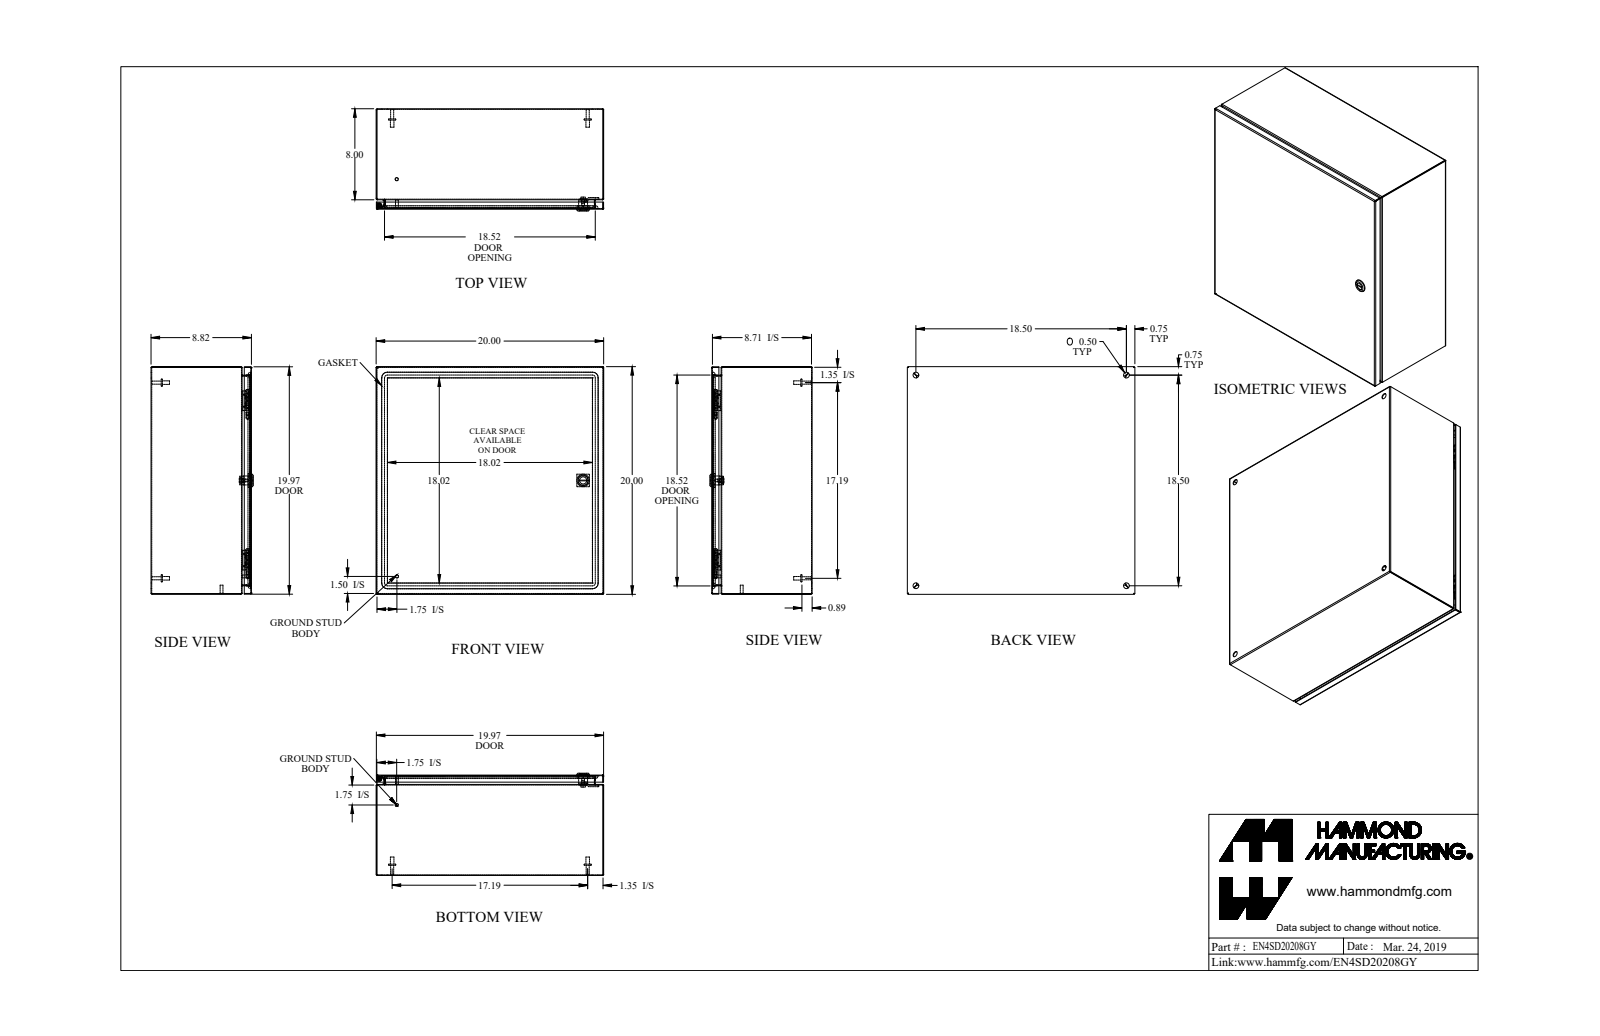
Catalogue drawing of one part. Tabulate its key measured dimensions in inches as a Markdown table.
| quantity | value |
| --- | --- |
| part name | EN4SD20208GY_Default |
| STEP written by | SolidWorks 2019 (CONFIG_CONTROL_DESIGN) |
| units | inches |
| bodies | 21 solids, 634 faces (285 planar, 213 cylindrical, 136 other) |
| overall size | 20 × 20 × 8.982 |
| volume | 98.82 in³ |
| surface area | 3 368 in² |
| round holes (diameter × count) | 0.5 × 4, 0.172 × 1, 0.232 × 1, 0.24 × 1, 0.242 × 1, 0.625 × 1, 0.785 × 1 |
| round bosses / shafts (diameter × count) | 0.625 × 4, 0.313 × 4, 0.27 × 4, 0.281 × 2, 0.25 × 2, 1.1 × 1, 0.525 × 1, 0.455 × 1 |
| partial cylindrical surfaces (radius × count) | 0.029 × 21, 0.086 × 21, 0.25 × 16, 19 × 8, 0.006 × 4, 0.062 × 4, 0.499 × 4, 0.125 × 2 |
| main face-to-face distances | 0.057, 8.765, 19.943, 8.708, 8.822, 19.886, 20, 0.822, 7.943, 0.749 |
| hole center spacings | 18.5, 26.163, 9.31, 9.311, 19.742, 19.742 |
